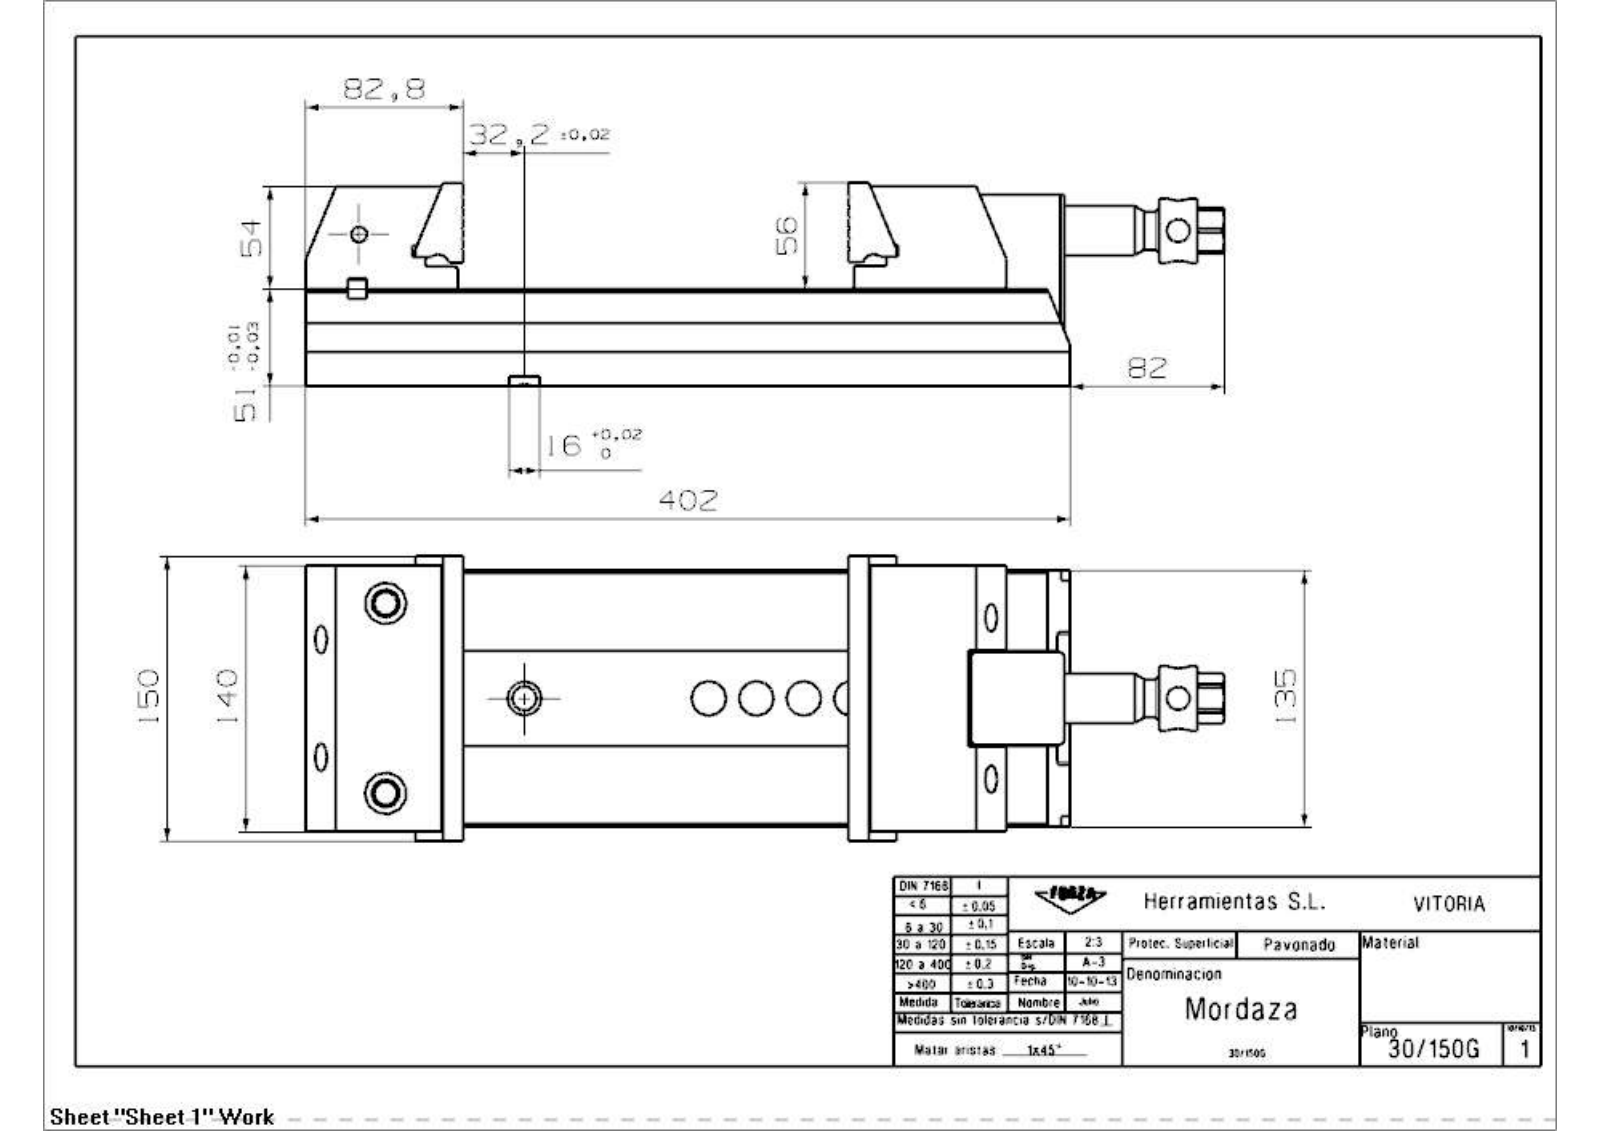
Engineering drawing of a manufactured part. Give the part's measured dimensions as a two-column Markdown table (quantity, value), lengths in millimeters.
| quantity | value |
| --- | --- |
| part name | 15091 Montaje taco atras; 30_150G_Mordaza |
| STEP written by | SIEMENS PLM Software NX 7.5 (CONFIG_CONTROL_DESIGN) |
| units | millimeters |
| bodies | 12 solids, 442 faces (292 planar, 98 cylindrical, 52 other) |
| overall size | 483 × 150 × 107.1 |
| volume | 3 179 000 mm³ |
| surface area | 449 091 mm² |
| round holes (diameter × count) | 13 × 6, 15 × 6, 5.19 × 5, 6.99 × 4, 8.5 × 4, 8.78 × 4, 10.58 × 4, 19 × 4, 9.7 × 2, 10 × 2, 12 × 2, 12.38 × 2 |
| round bosses / shafts (diameter × count) | 34 × 1, 33.8 × 1, 26 × 1, 20 × 1, 16.5 × 1 |
| partial cylindrical surfaces (radius × count) | 1.5 × 4, 8 × 4, 20 × 4, 1.6 × 2, 5.5 × 2, 6 × 2, 4 × 1, 9 × 1 |
| main face-to-face distances | 51, 19.3, 31.7, 105, 49.4, 8, 1.6, 17.7, 135, 2.5 |
| hole center spacings | 11.5, 73.5, 85, 11.51, 95.17, 11.46, 22.27, 27.2 |
